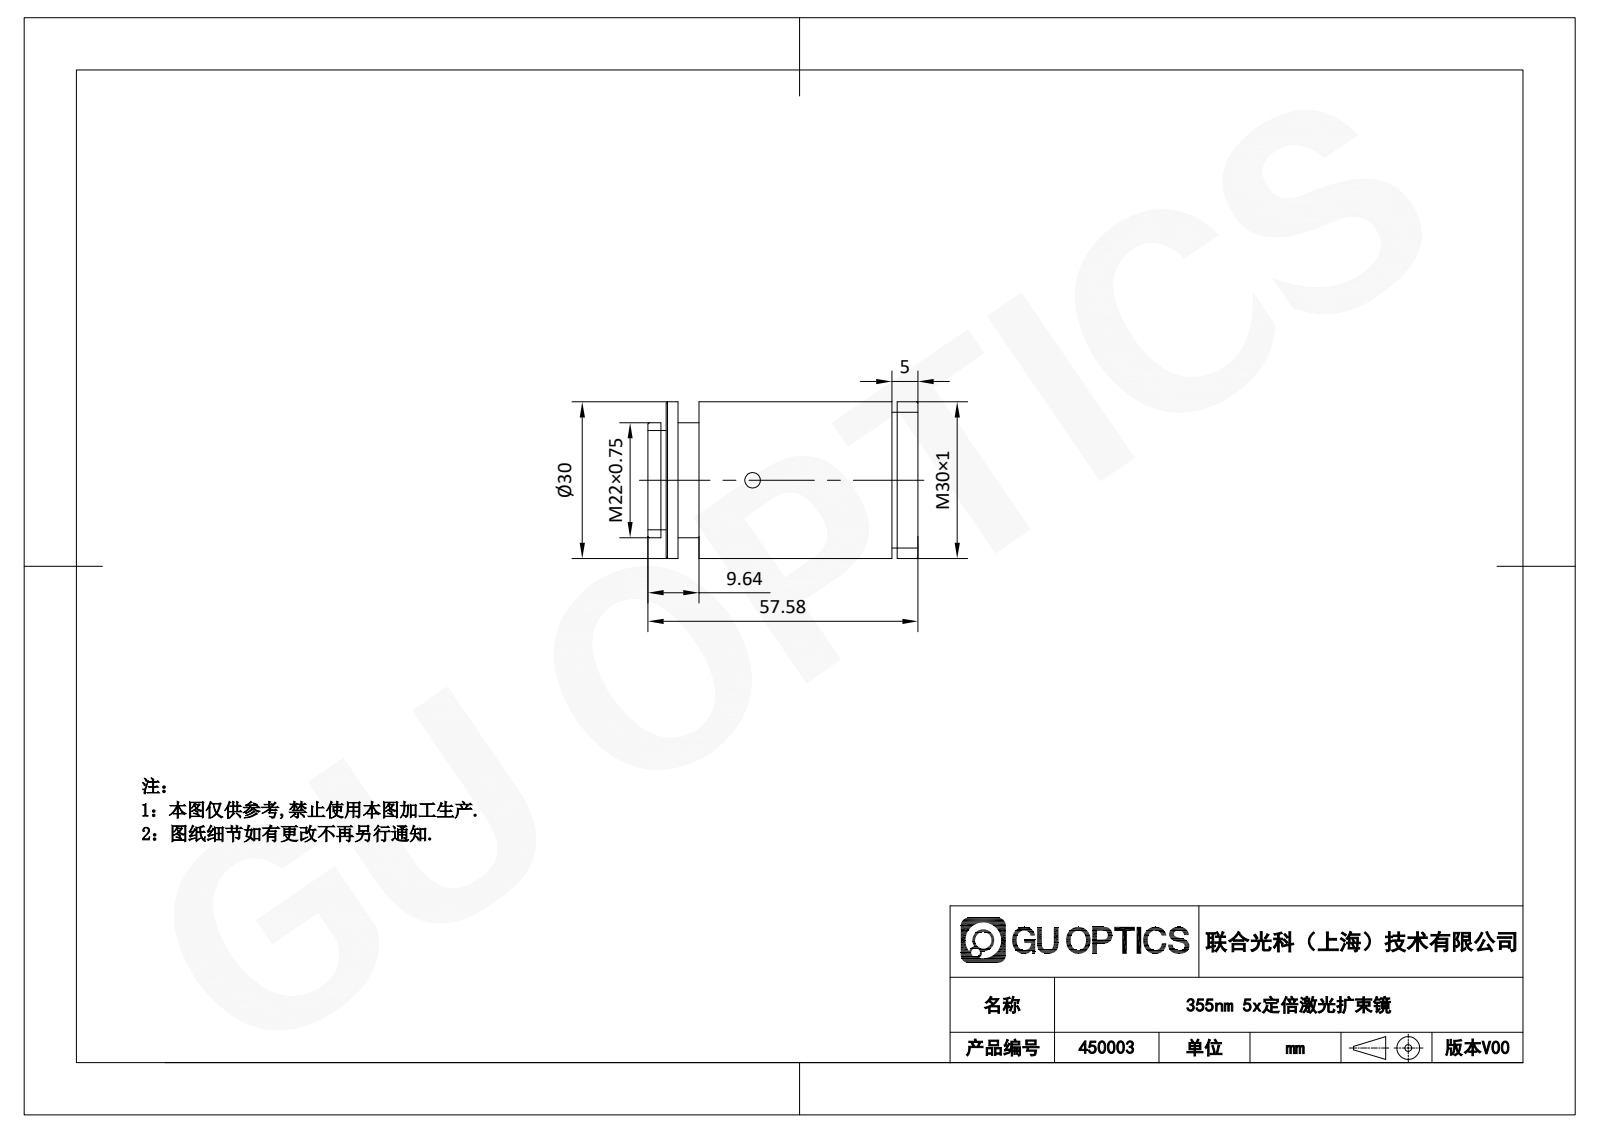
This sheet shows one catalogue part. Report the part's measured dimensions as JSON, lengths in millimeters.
{"part_name": "450003", "step_written_by": "SolidWorks 2020 (AUTOMOTIVE_DESIGN)", "units": "millimeters", "bodies": {"solids": 1, "faces": 43, "planar": 11, "cylindrical": 22, "other": 10}, "overall_size": [57.58, 30, 30], "volume_mm3": 30853, "surface_area_mm2": 10401, "round_holes": [[8, 1], [18, 1]], "round_bosses_or_shafts": [[30, 1], [26, 1], [22, 1], [19, 1]], "face_to_face_distances": [4, 47.94, 50.08, 54.08, 2.14, 51.94, 6.14, 43.94, 3.5, 5.64]}
